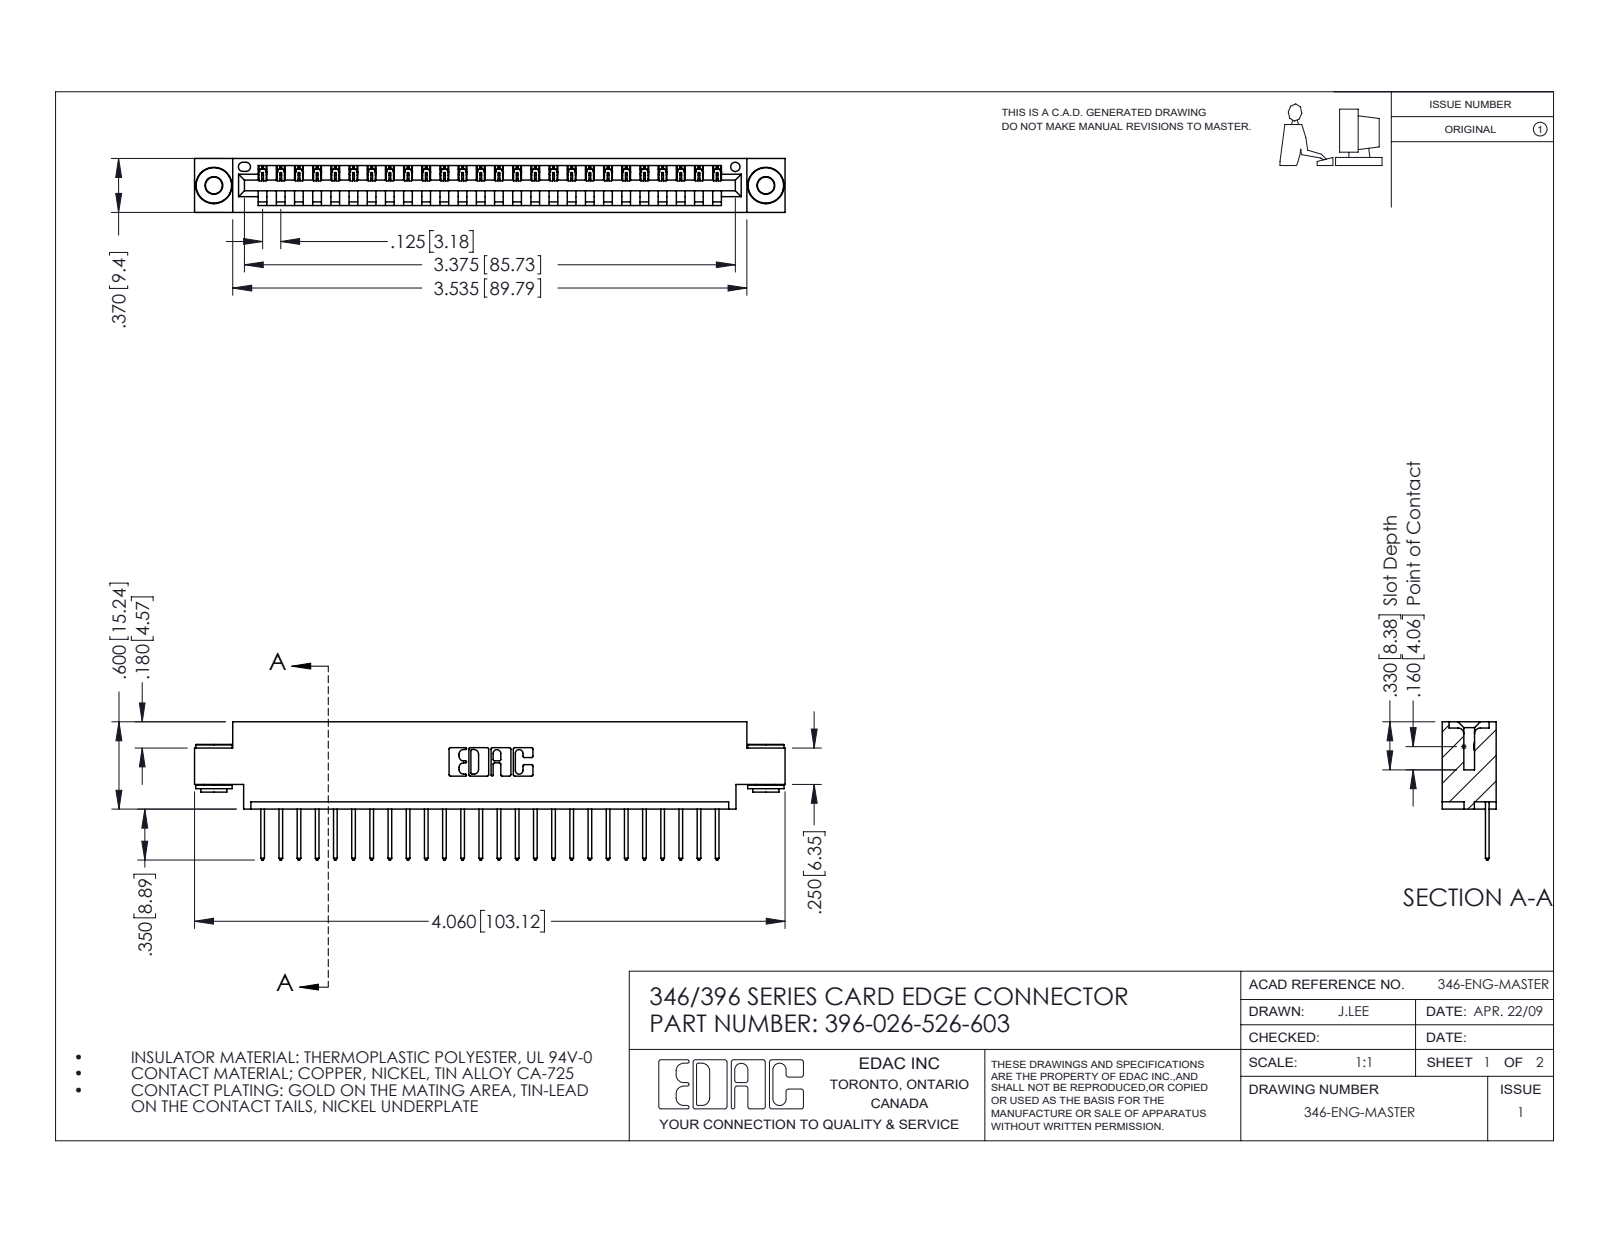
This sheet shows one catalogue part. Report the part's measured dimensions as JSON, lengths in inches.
{"part_name": "346 Part_0.170 Offset - 0.156 Dia-TH; 345-292-001_345-293-126; 345-250-002_345-250-002-102; 396-026-526-603", "step_written_by": "SolidWorks 2016 (CONFIG_CONTROL_DESIGN)", "units": "inches", "bodies": {"solids": 29, "faces": 1672, "planar": 1130, "cylindrical": 534, "other": 8}, "overall_size": [4.06, 0.95, 0.37], "volume_in3": 0.586, "surface_area_in2": 18.89, "round_holes": [[0.116, 2], [0.156, 2], [0.064, 1]], "round_bosses_or_shafts": [[0.25, 2], [0.18, 2], [0.136, 2]], "partial_cylinders_radius": [[0.006, 52], [0.01, 52], [0.01, 22], [0.007, 6], [0.031, 6], [0.026, 3], [0.031, 2], [0.04, 2]], "face_to_face_distances": [0.048, 0.322, 0.37, 0.25, 0.025, 0.072, 0.298, 0.148, 0.222, 0.1], "hole_center_spacings": [0.246, 3.587, 3.795]}
